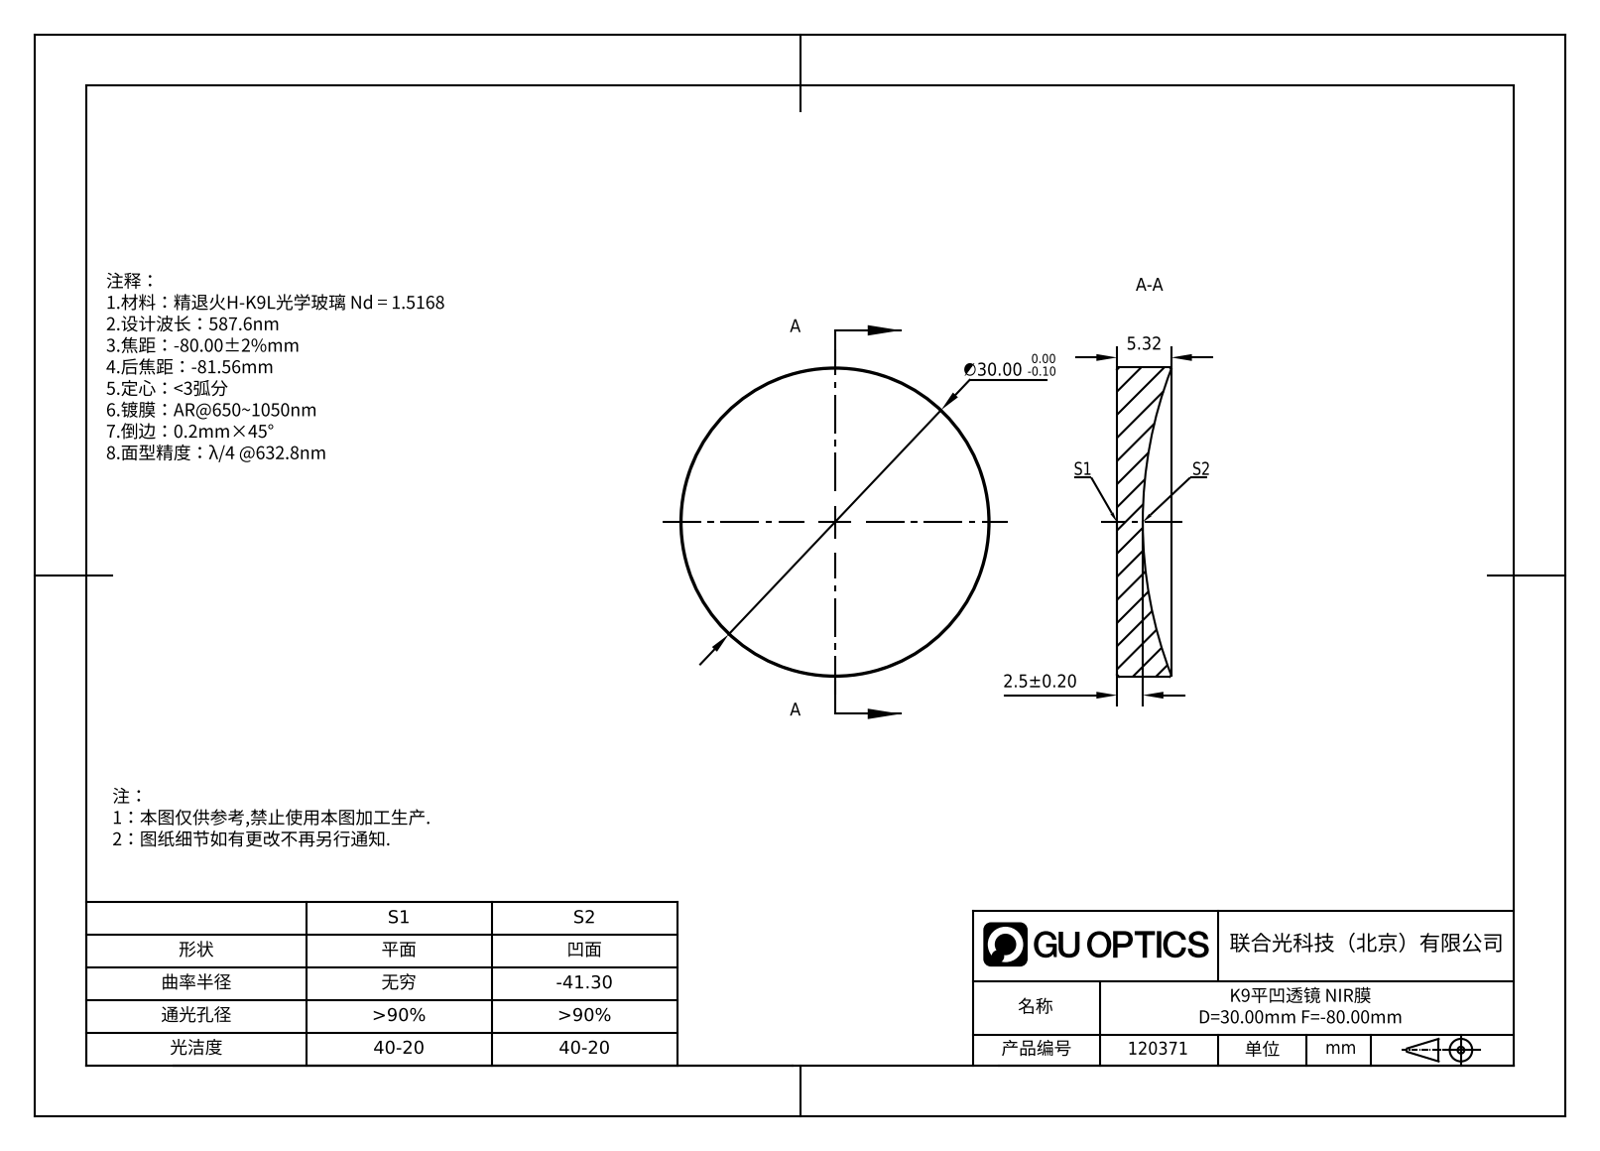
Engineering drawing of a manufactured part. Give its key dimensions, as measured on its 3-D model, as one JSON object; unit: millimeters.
{"part_name": "GL13-030-080", "step_written_by": "SolidWorks 2022 (AUTOMOTIVE_DESIGN)", "units": "millimeters", "bodies": {"solids": 1, "faces": 9, "planar": 1, "cylindrical": 2, "other": 6}, "overall_size": [30, 30, 5.26], "volume_mm3": 2749, "surface_area_mm2": 1915, "round_bosses_or_shafts": [[30, 1]]}
